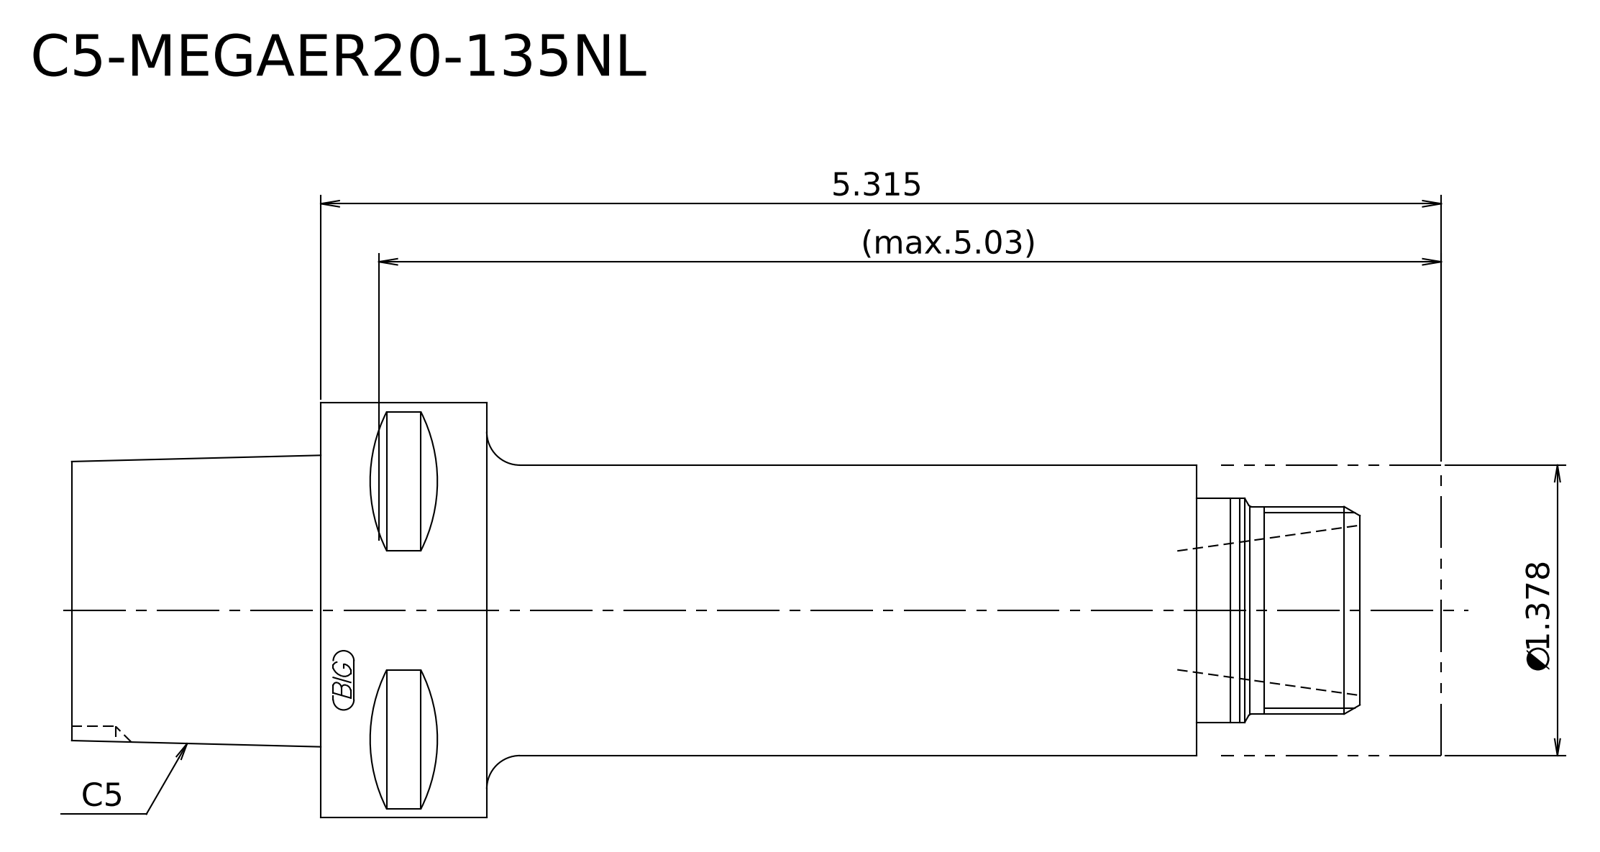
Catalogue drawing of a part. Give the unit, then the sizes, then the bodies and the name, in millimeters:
Units: millimetres
Overall size (bounding box): 165 × 50 × 50
Round bosses / shafts (diameter × count): ⌀50 ×1, ⌀35 ×1, ⌀27 ×1, ⌀25 ×1
Main face-to-face distances: 108.5, 26.5, 135, 165, 138.5, 30, 115, 88.5, 20, 50
Volume: 185 265 mm³ · Surface area: 25 716 mm²
Bodies: 2 solids, 16 faces (7 planar, 5 cylindrical, 4 other)
STEP written by: Kubotek KeyCreator 2011 V10.0.2 (22737) (automotive_design)
